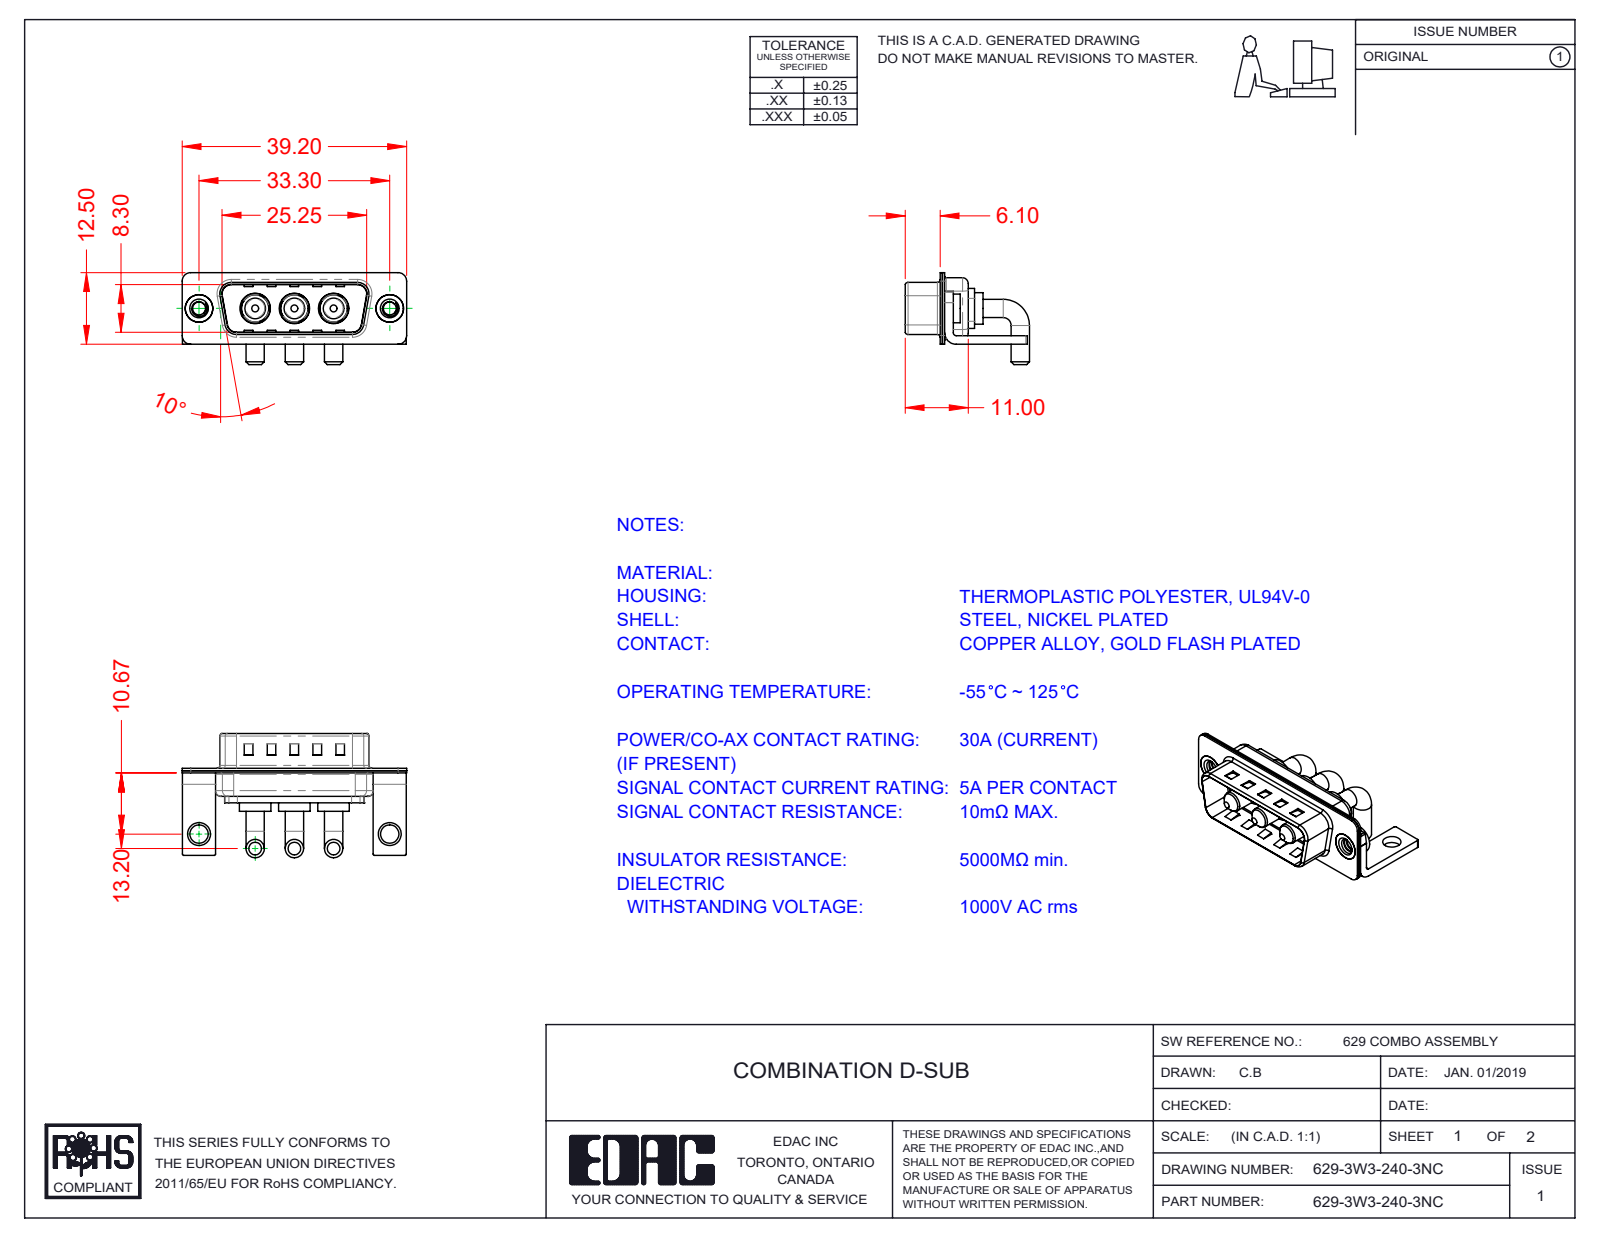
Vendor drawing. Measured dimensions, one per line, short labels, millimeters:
name: 629Combo Shell Front_15 Contacts; Power Pin_30A RA; 629Combo Shell Rear_15 Contacts; 629Combo Threaded Rivet_2 (+3 more)
written by: SolidWorks 2020 (CONFIG_CONTROL_DESIGN)
unit: mm
bodies: 13 solids, 517 faces (189 planar, 220 cylindrical, 108 other)
size: 39.2 × 21.7 × 16.05
volume: 2 648 mm³; area: 5 687 mm²
holes: 3× ⌀4.85, 3× ⌀5.3, 2× ⌀2.26, 2× ⌀3.2, 2× ⌀4, 2× ⌀4.8
bosses: 6× ⌀3.2, 3× ⌀5.5, 3× ⌀5.2, 3× ⌀4.75, 3× ⌀3.75, 3× ⌀3.6, 2× ⌀5, 2× ⌀4.9
rounds: 16× R0.25, 16× R1.5, 13× R2, 9× R0.5, 8× R1.6, 4× R0.6, 4× R0.65, 4× R0.9
face distances: 0.4, 0.8, 1.5, 9.5, 9.1, 8.7, 9.9, 5.2, 1.2, 0.75
hole spacings: 6.85, 9.8, 16.65, 23.5, 33.3, 13.7
